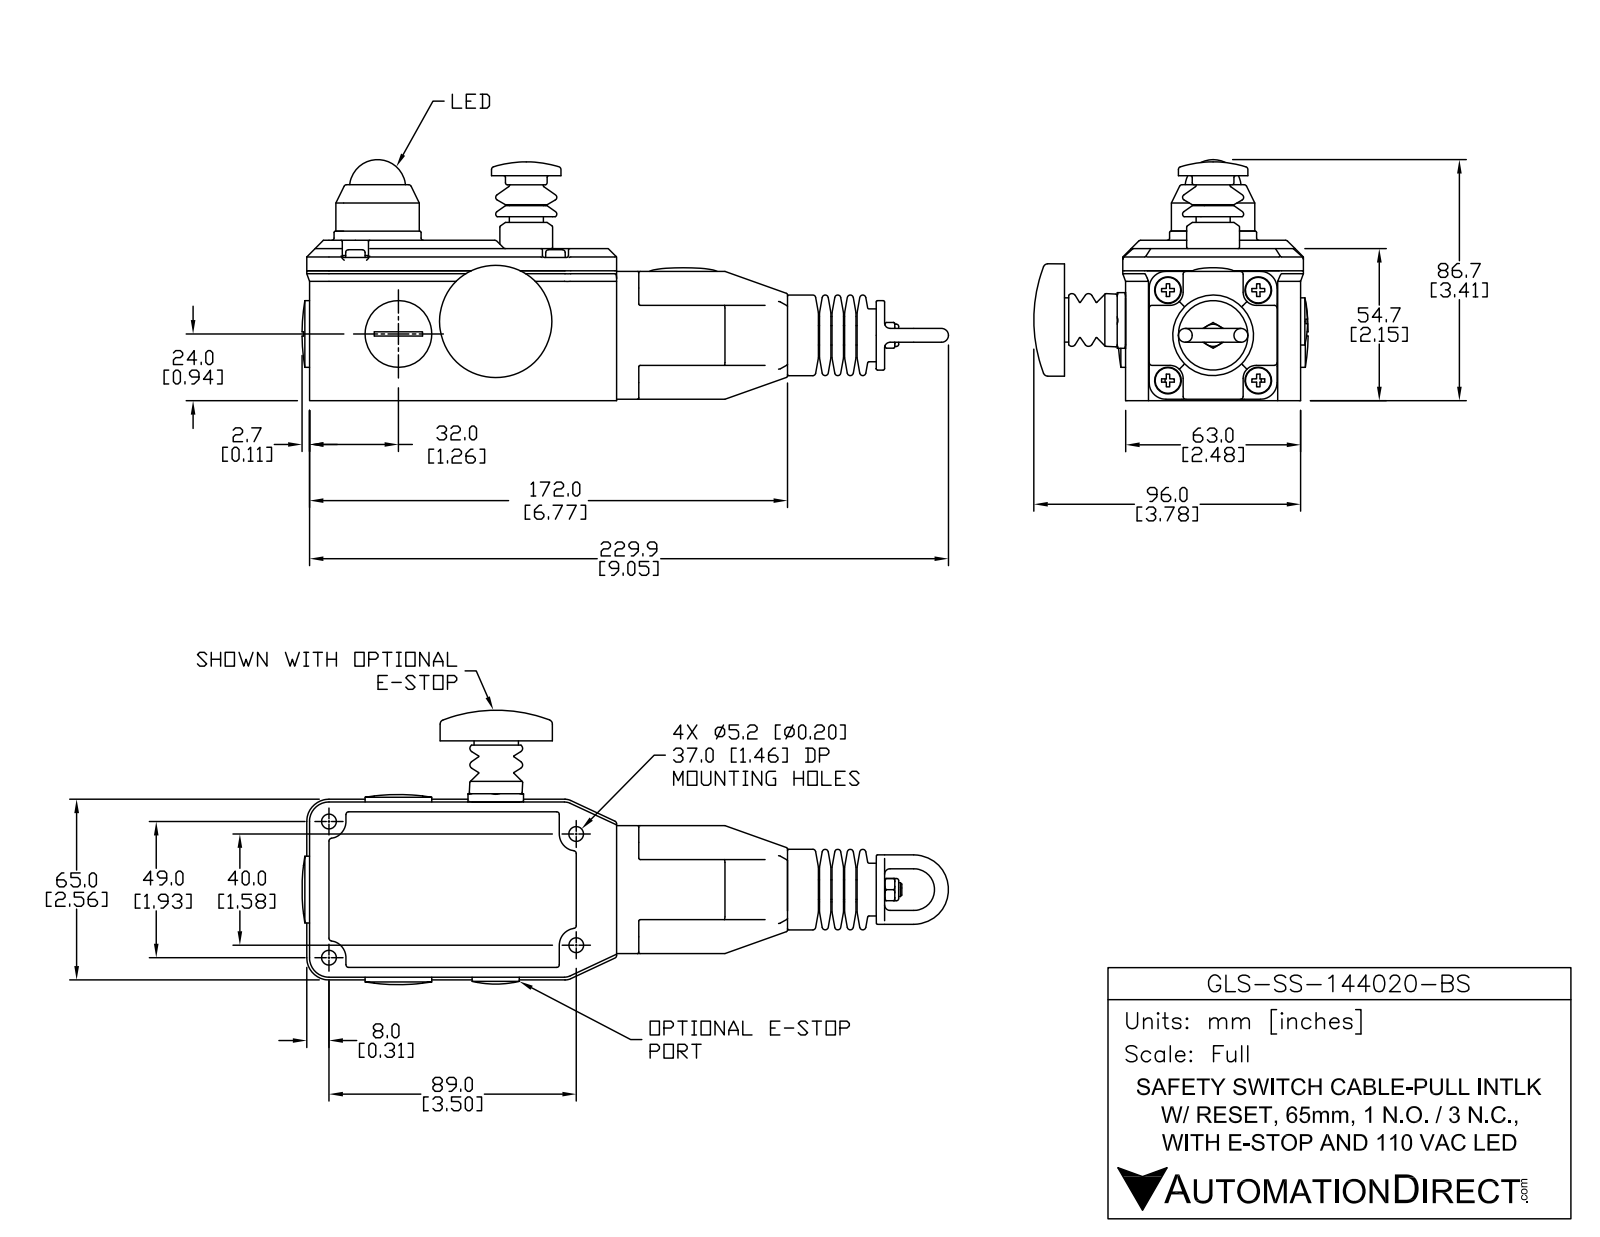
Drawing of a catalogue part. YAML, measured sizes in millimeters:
part_name: "GLS-SS-144020-BS"
step_written_by: "SolidWorks 2013 (AUTOMOTIVE_DESIGN)"
units: millimeters
bodies: {solids: 2, faces: 685, planar: 204, cylindrical: 236, other: 245}
overall_size: [233.8, 104.37, 86]
volume: 527351
surface_area: 65123
round_holes:
  - {diameter: 5.2, count: 4}
  - {diameter: 9.5, count: 4}
  - {diameter: 21, count: 1}
round_bosses_or_shafts:
  - {diameter: 9.2, count: 4}
  - {diameter: 6, count: 4}
  - {diameter: 26.8, count: 2}
  - {diameter: 25, count: 2}
  - {diameter: 19, count: 2}
  - {diameter: 5, count: 2}
  - {diameter: 40, count: 1}
  - {diameter: 31.3, count: 1}
partial_cylinders:
  - {radius: 0.5, count: 74}
  - {radius: 0.75, count: 20}
  - {radius: 1, count: 8}
  - {radius: 3, count: 4}
  - {radius: 4.5, count: 4}
  - {radius: 4.8, count: 4}
  - {radius: 5, count: 4}
  - {radius: 16, count: 4}
face_to_face_distances: [54.4, 65, 54.7, 11.7, 33.3, 45, 90.65, 25.65, 4.5, 9.98]
hole_center_spacings: [32.5, 32.6, 46.03, 89.11, 99.51, 28.87, 29.27, 40]
